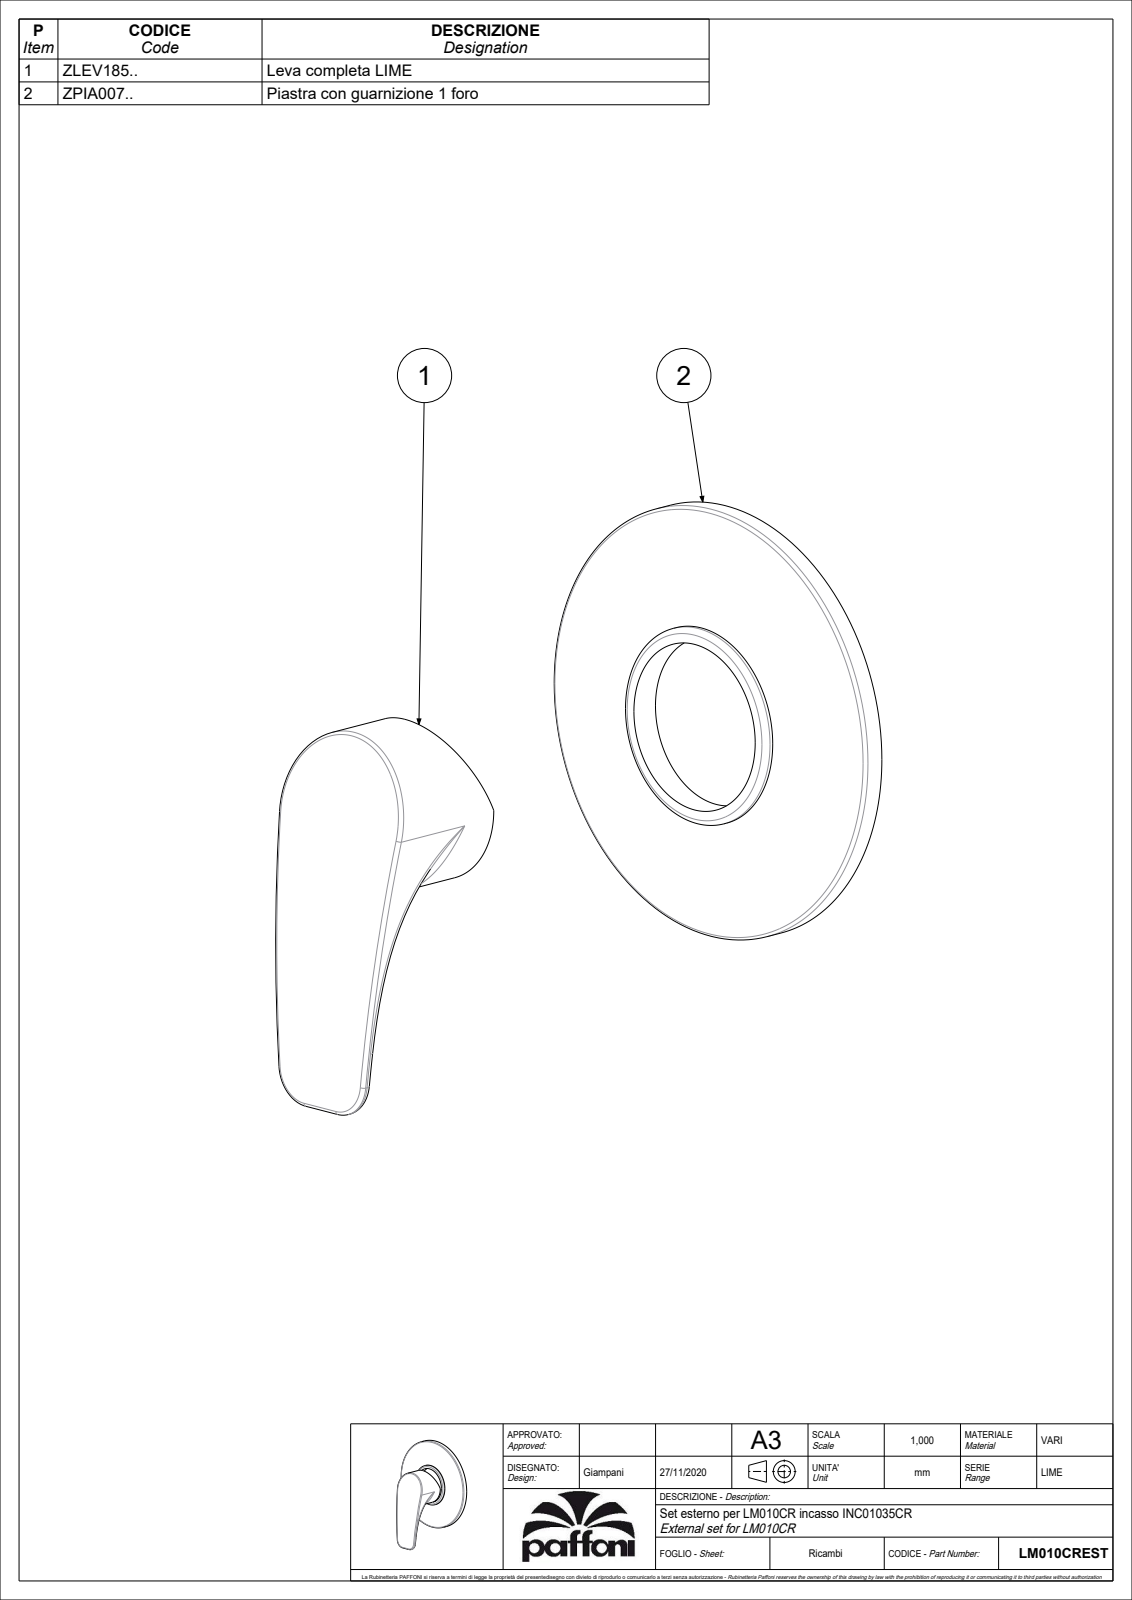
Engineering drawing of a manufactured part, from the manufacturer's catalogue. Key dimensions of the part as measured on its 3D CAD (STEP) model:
Part name (STEP PRODUCT): LM010CREST
STEP written by: CREO PARAMETRIC BY PTC INC, 2020044 (CONFIG_CONTROL_DESIGN)
Units: millimetres
Bodies: 2 solids, 157 faces (49 planar, 56 cylindrical, 52 other)
Overall size (bounding box): 136 × 116 × 55.5
Volume: 37 245 mm³ · Surface area: 42 629 mm²
Round holes (diameter × count): ⌀3 ×1, ⌀45 ×1, ⌀50 ×1, ⌀114 ×1
Round bosses / shafts (diameter × count): ⌀116 ×1, ⌀53 ×1, ⌀7.6 ×1, ⌀5.5 ×1, ⌀5 ×1
Partial cylindrical surfaces — rounded edges, fillets, slot ends (radius × count): R1 ×12, R10 ×2, R2 ×1, R354.51 ×1, R423.84 ×1, R426.84 ×1
Main face-to-face distances: 4, 9.1, 11.5, 2.5, 3.5, 8, 7.5, 9, 5.5, 1.5
